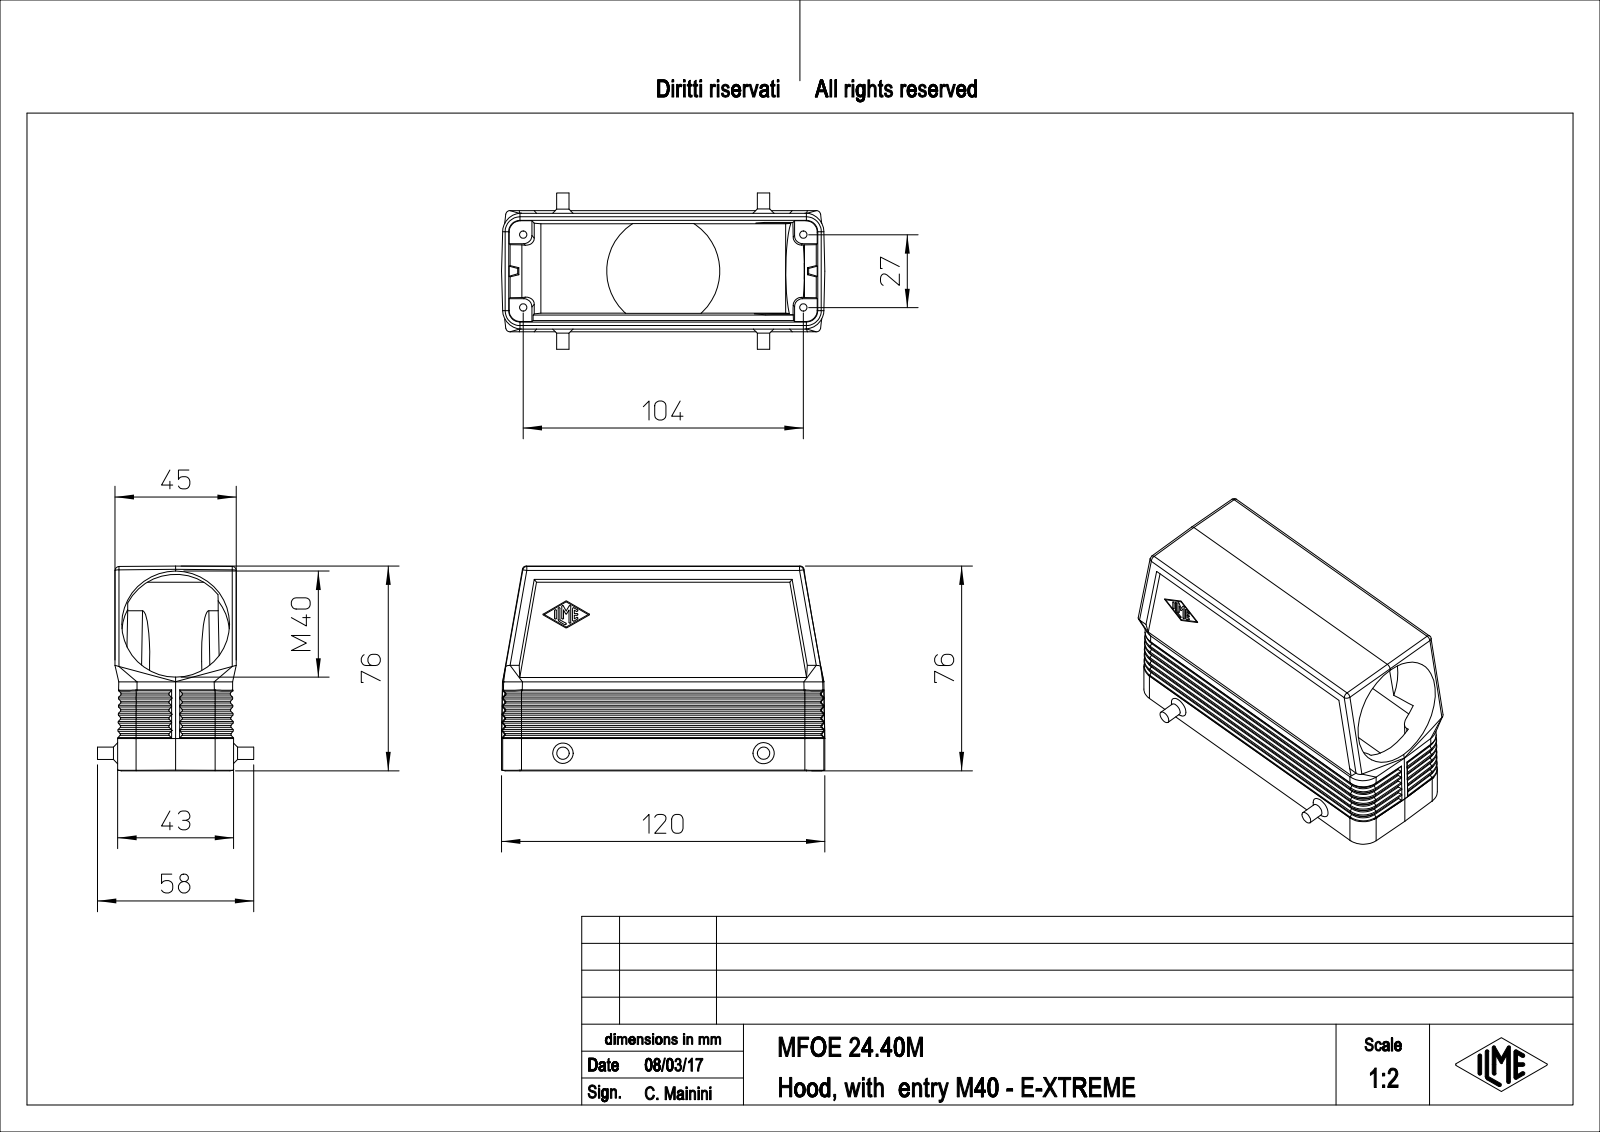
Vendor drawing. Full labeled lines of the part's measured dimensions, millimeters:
Part name (STEP PRODUCT): MFOE_24.40M
STEP written by: PTC Creo Elements/Direct Modeling 19.0E 27-Jun-2016 (C) Parametric Technology GmbH (AUTOMOTIVE_DESIGN)
Units: millimetres
Bodies: 1 solid, 478 faces (210 planar, 132 cylindrical, 136 other)
Overall size (bounding box): 120 × 76 × 58
Volume: 100 842 mm³ · Surface area: 53 548 mm²
Round holes (diameter × count): ⌀2.75 ×4, ⌀40 ×1
Round bosses / shafts (diameter × count): ⌀4.59 ×2
Partial cylindrical surfaces — rounded edges, fillets, slot ends (radius × count): R0.5 ×78, R1.5 ×10, R7 ×8, R3 ×4, R4.2 ×4, R21 ×1
Main face-to-face distances: 43, 2.01, 2, 4, 3.2, 1, 44, 6, 8.45, 6.01
Hole centre spacings: 27, 104, 107.45
